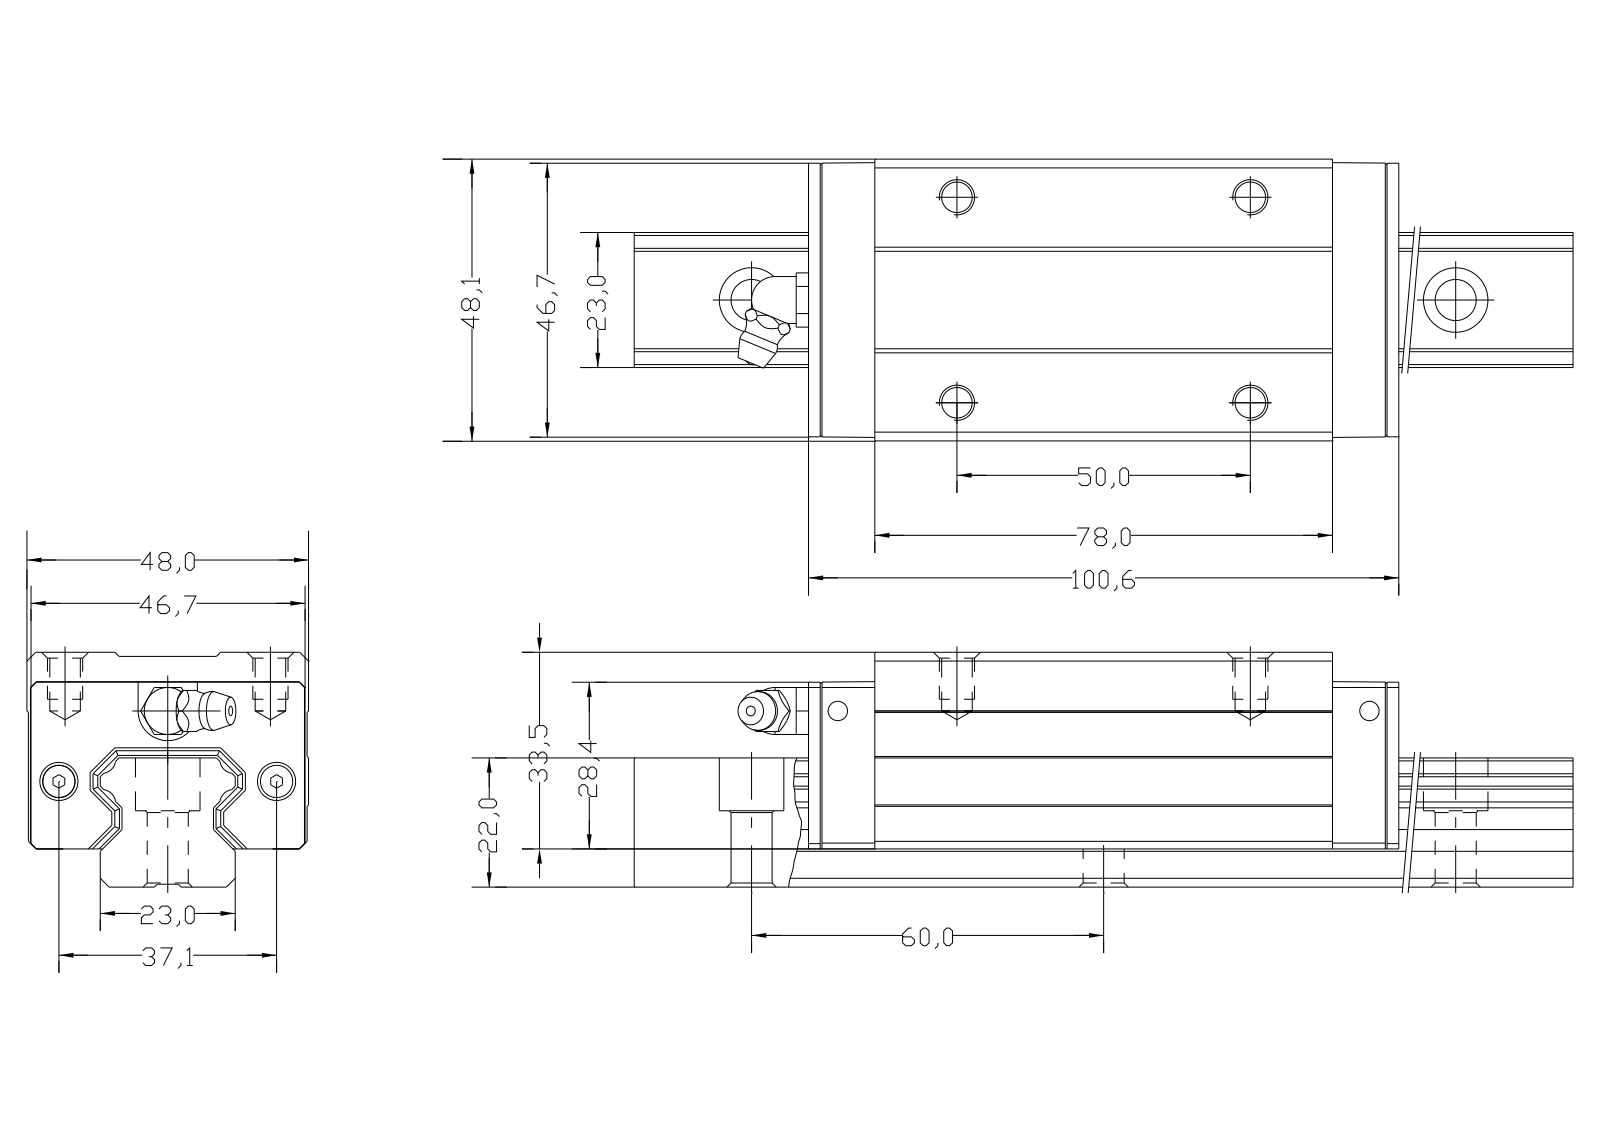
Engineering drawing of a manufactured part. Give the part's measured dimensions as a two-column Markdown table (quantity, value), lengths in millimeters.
| quantity | value |
| --- | --- |
| STEP written by | Kubotek KeyCreator V6.5.2 (0407) (CONFIG_CONTROL_DESIGN) |
| units | millimeters |
| bodies | 3 solids, 209 faces (136 planar, 56 cylindrical, 17 other) |
| overall size | 220 × 48 × 40 |
| volume | 212 390 mm³ |
| surface area | 46 944 mm² |
| round holes (diameter × count) | 6 × 4, 7 × 4, 11 × 4, 6.5 × 3, 3.25 × 2 |
| round bosses / shafts (diameter × count) | 8 × 1 |
| partial cylindrical surfaces (radius × count) | 2.65 × 4, 5.05 × 1 |
| main face-to-face distances | 22, 6.5, 0.7, 15.5, 16.02, 31.48, 33.5, 40, 18, 12.25 |
| hole center spacings | 18.2, 57.72, 67.31, 116.32, 60, 22.09, 35, 50 |
